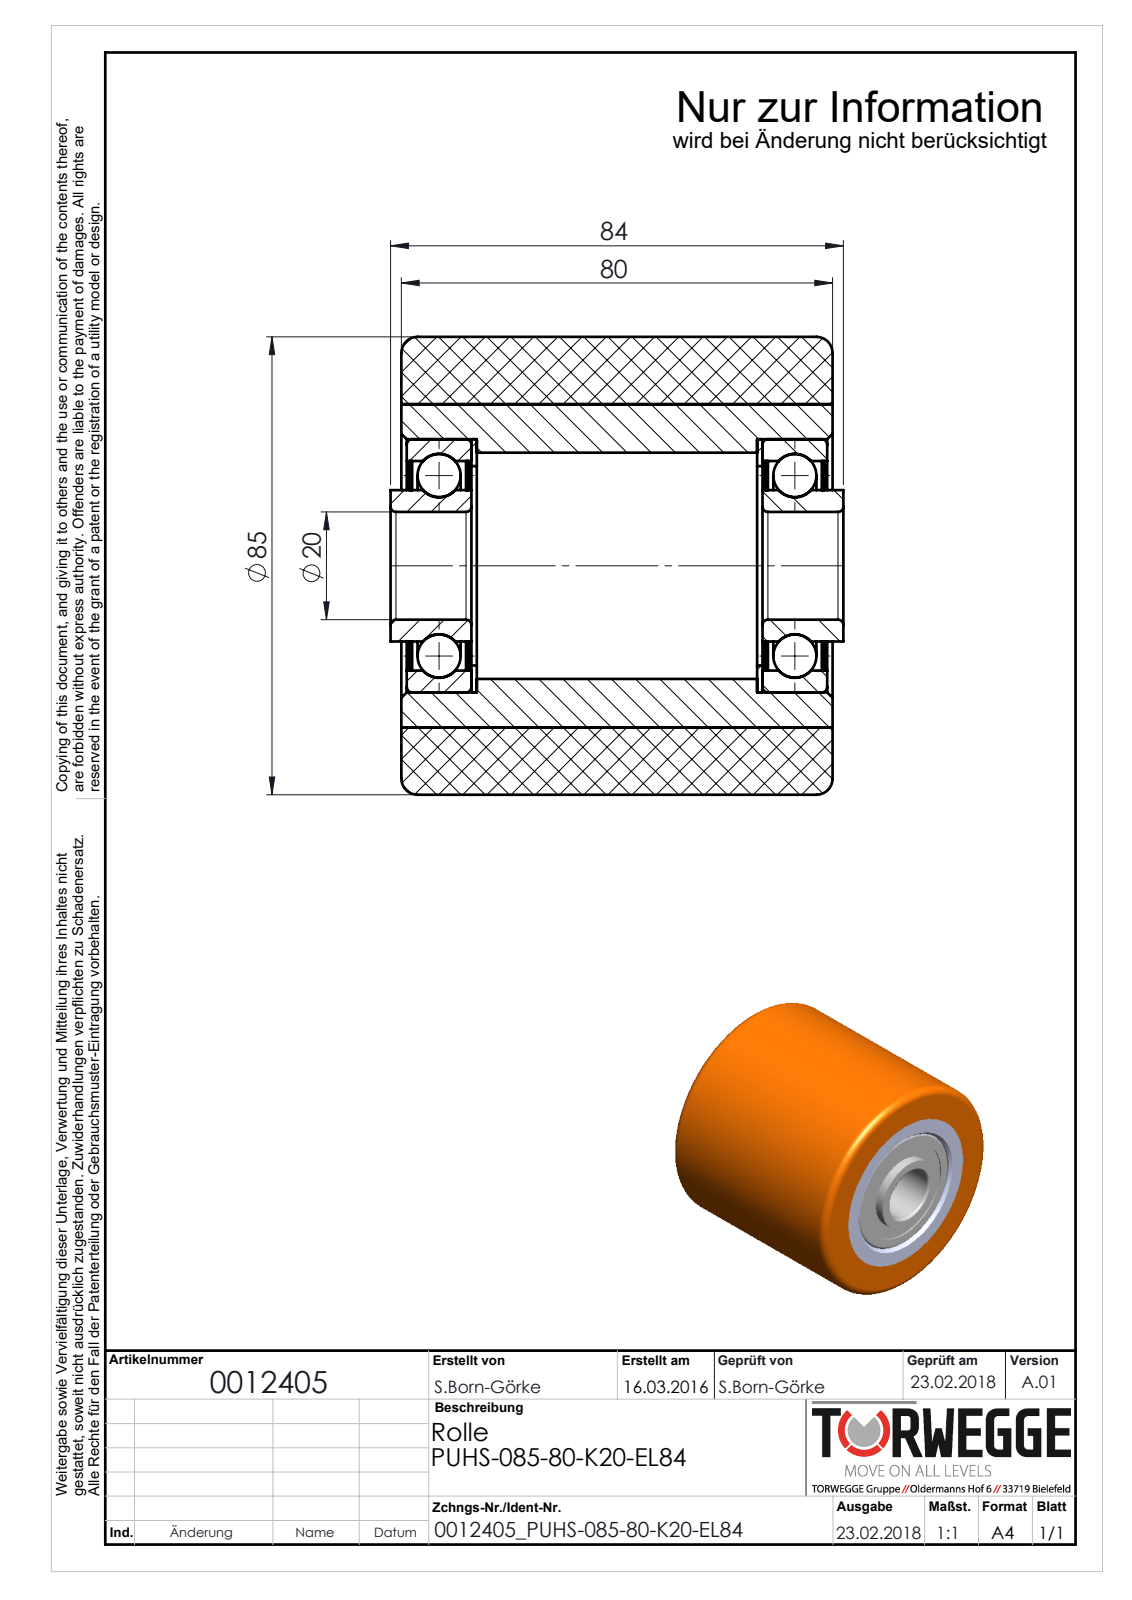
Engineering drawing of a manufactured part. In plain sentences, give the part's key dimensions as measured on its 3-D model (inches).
The part is named "0012405_PUHS-085-80-K20-EL84". Its 3-D file was written by "SolidWorks 2016 (AUTOMOTIVE_DESIGN)". It is 0 solids with 54 faces: 10 planar, 24 cylindrical and 20 other. Overall it measures 3.346 by 3.346 by 3.307 inches. Round holes: 1 of diameter 0.787, 1 of diameter 1.531, 1 of diameter 1.654, 1 of diameter 1.85, 1 of diameter 2.362. Round bosses or shafts: 1 of diameter 3.346, 1 of diameter 1.106. The main face-to-face distances are 3.15, 0.059, 3.091, 0.039, 3.11, 0.02, 3.051, 3.031, 0.079, 0.118.
